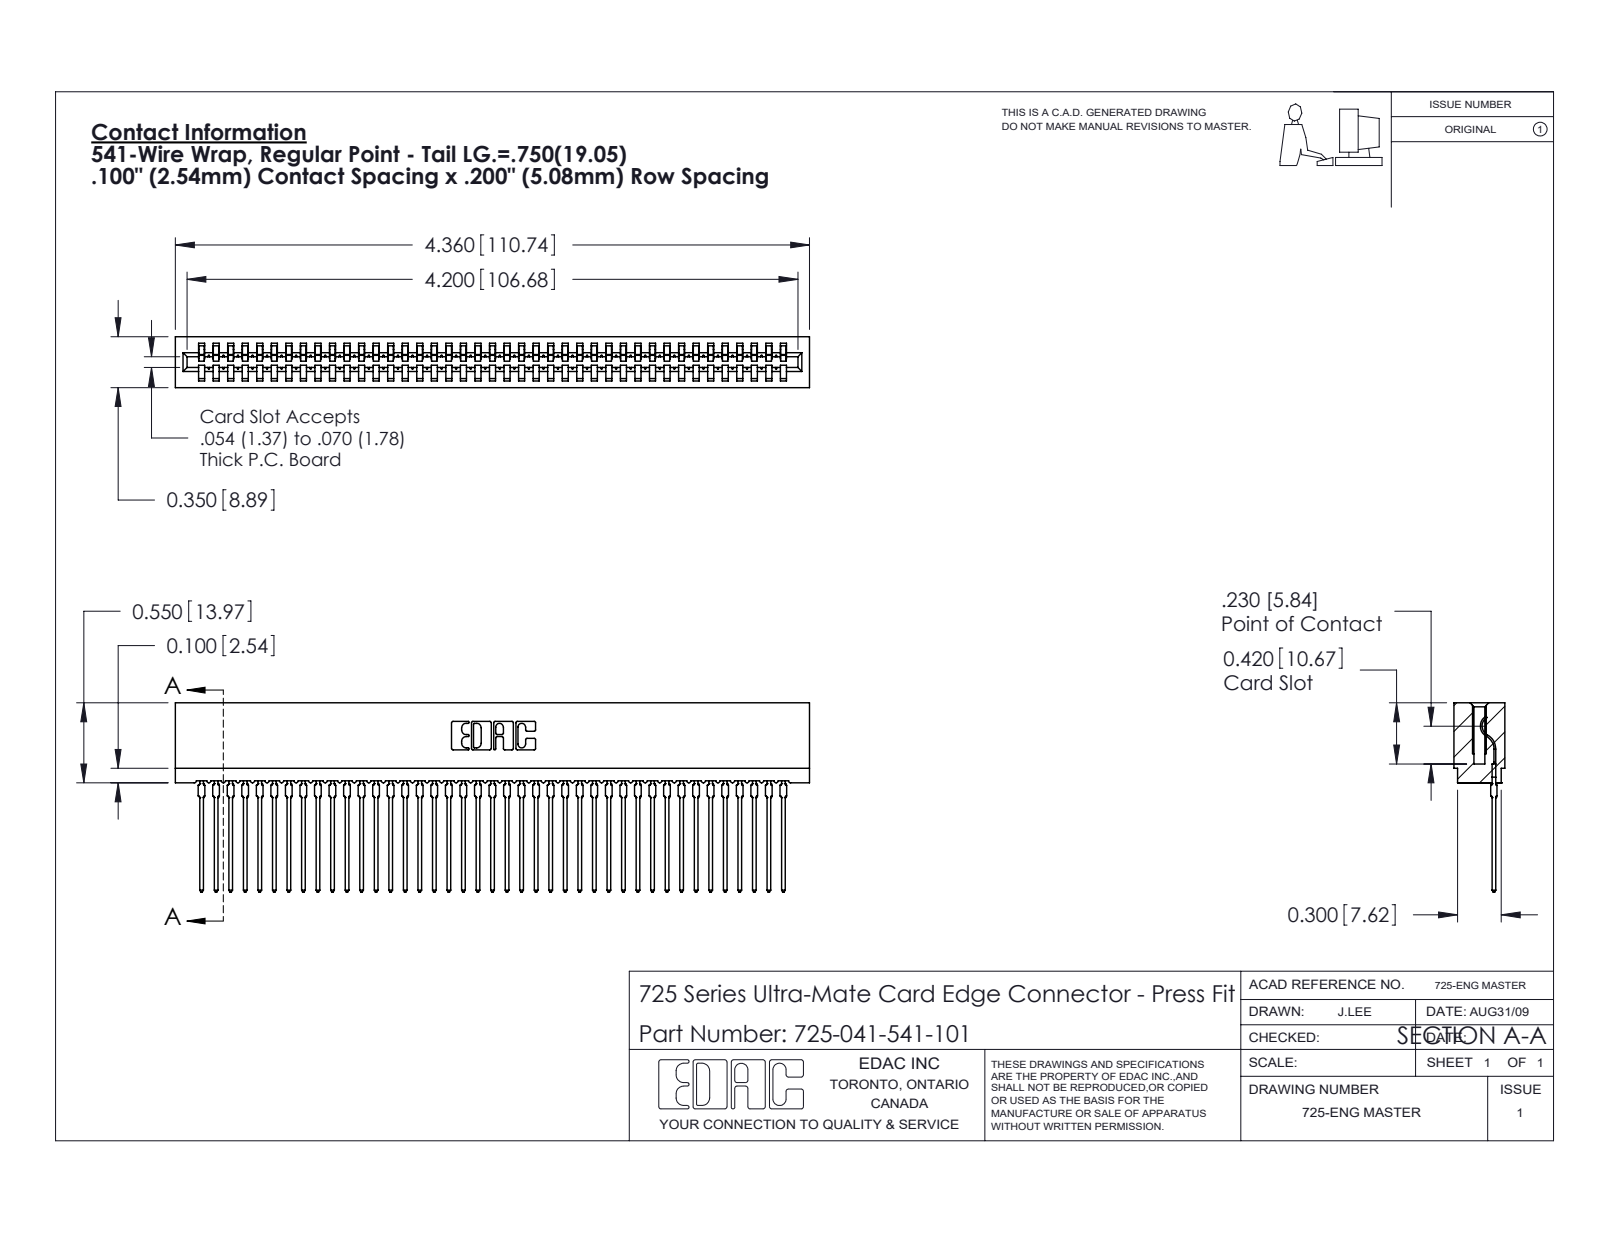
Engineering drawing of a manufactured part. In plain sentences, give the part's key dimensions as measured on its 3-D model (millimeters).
The part is named "725 Part_Insulator Option - 01; 745-292-001_541; 725-041-541-101". Its 3-D file was written by "SolidWorks 2020 (CONFIG_CONTROL_DESIGN)". It is 42 solids with 4687 faces: 2802 planar, 819 cylindrical and 1066 other. Overall it measures 110.7 by 33 by 8.9 millimeters. Its volume is 8 590 cubic millimeters and its surface area 17 300 square millimeters. Partial cylindrical surfaces (rounded edges, fillets, slot ends): 82 of radius 0.4, 82 of radius 0.5, 22 of radius 0.3, 6 of radius 0.2, 6 of radius 0.8, 4 of radius 0.1, 4 of radius 0.3, 3 of radius 0.7. The main face-to-face distances are 8.9, 5.1, 1.6, 7.3, 2.5, 5.4, 3.5, 1.1, 7.7, 2.4.
